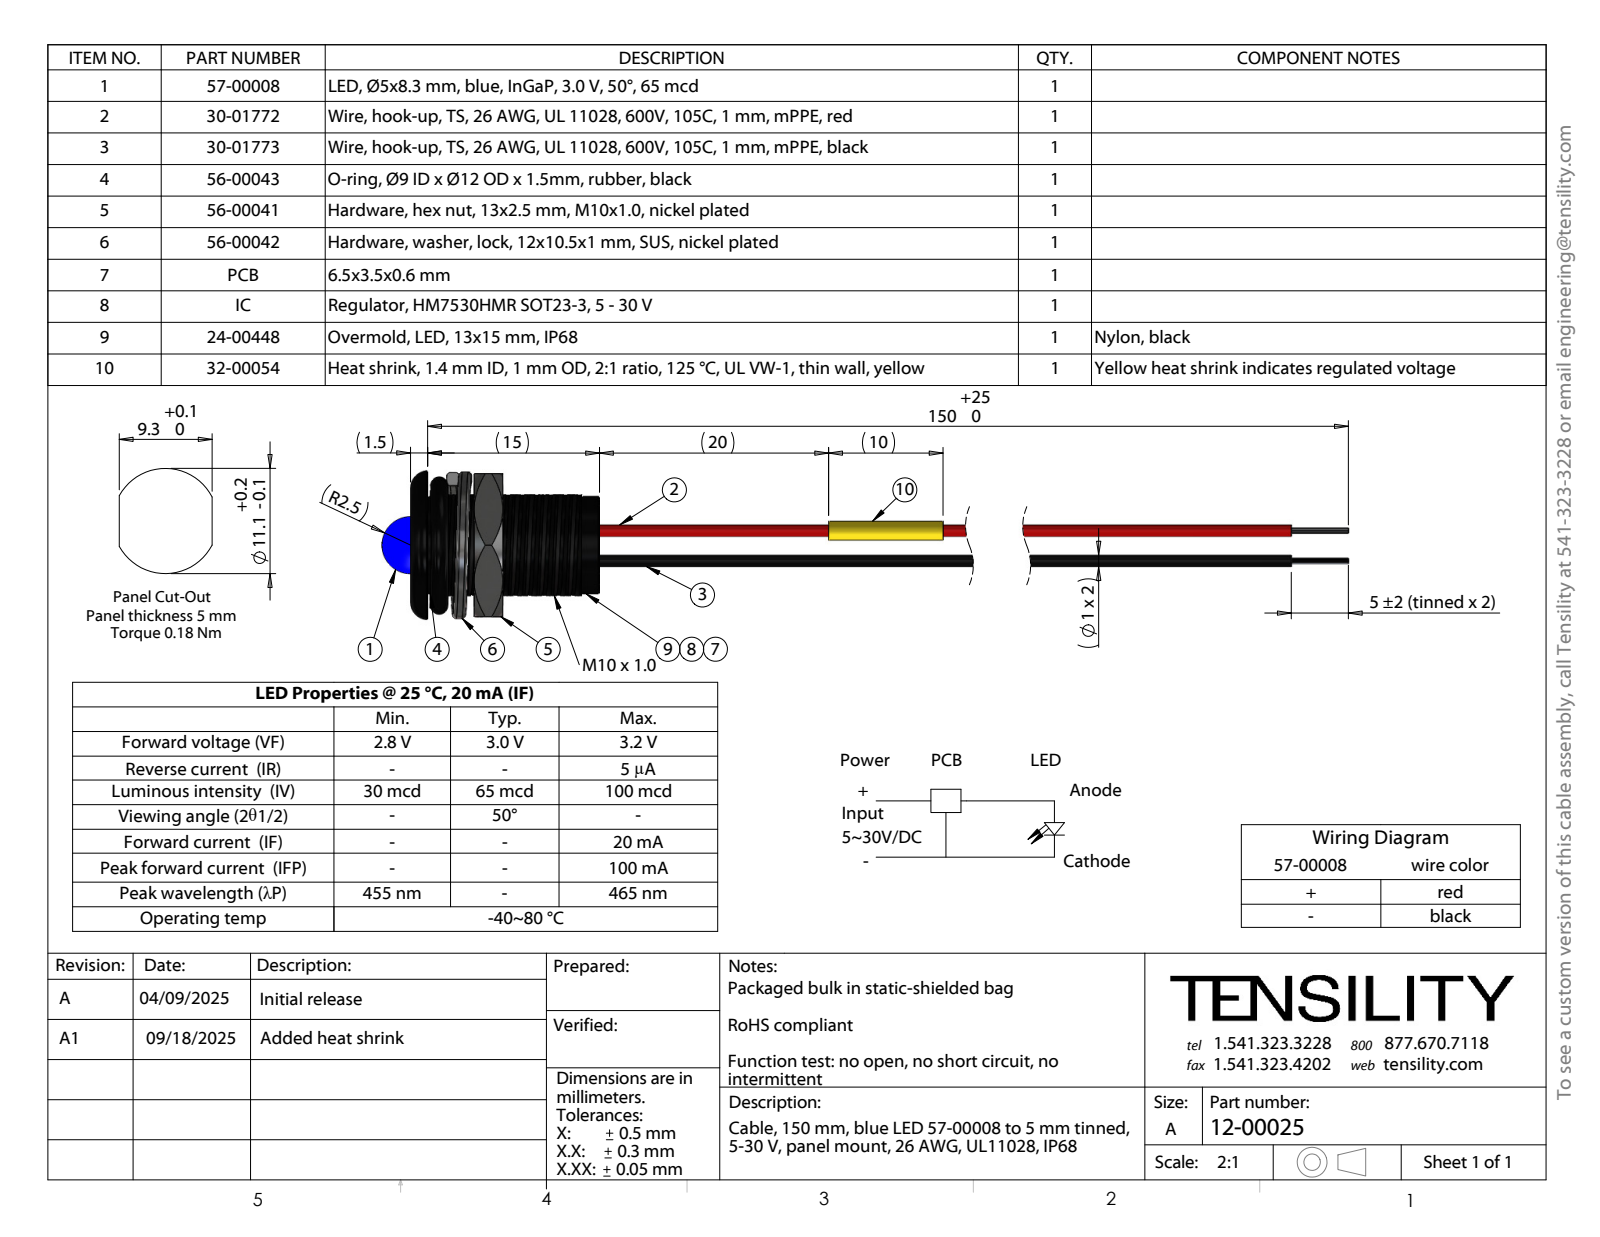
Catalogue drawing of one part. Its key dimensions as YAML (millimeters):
part_name: "30-01772_stripped and tinned; 56-00042_Split washer; 57-00008_trimmed leads; 30-01773_stripped and tinned (+4 more)"
step_written_by: "SolidWorks 2021 (CONFIG_CONTROL_DESIGN)"
units: millimeters
bodies: {solids: 57, faces: 514, planar: 185, cylindrical: 246, other: 83}
overall_size: [173.99, 14.43, 12.99]
volume: 1769
surface_area: 6568
round_holes:
  - {diameter: 1, count: 2}
round_bosses_or_shafts:
  - {diameter: 1, count: 2}
  - {diameter: 0.83, count: 2}
  - {diameter: 8.5, count: 1}
  - {diameter: 5, count: 1}
partial_cylinders:
  - {radius: 4.33, count: 1}
  - {radius: 5, count: 1}
face_to_face_distances: [1.5, 16.5, 15, 12.5, 8.06, 6.56, 8.44, 5.56, 4.06, 2.5]
hole_center_spacings: [0.36, 0.38, 0.33, 2.43, 2.35, 2.48, 2.52, 2.56]
